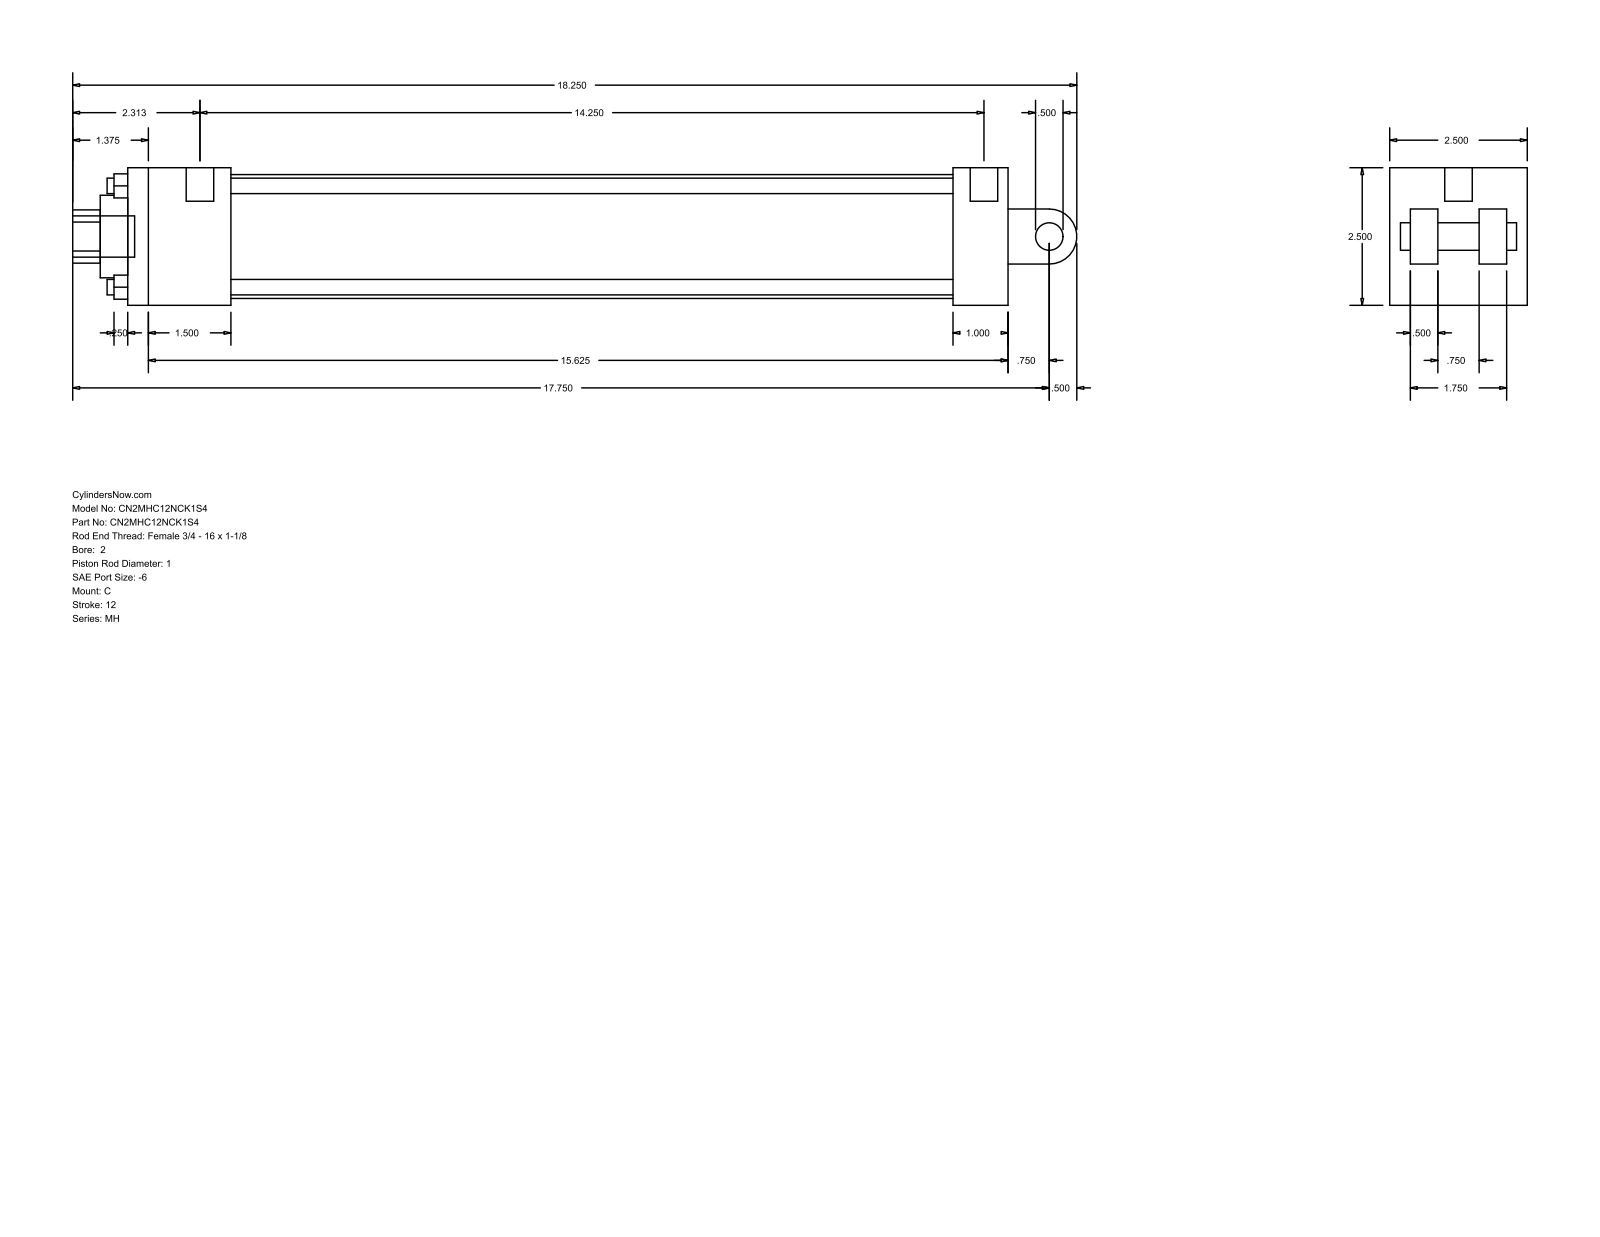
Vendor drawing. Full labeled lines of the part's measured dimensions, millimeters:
Part name (STEP PRODUCT): MH_C__0200_1
STEP written by: GSSL Pune (CONFIG_CONTROL_DESIGN)
Units: millimetres
Bodies: 0 solids, 99 faces (70 planar, 29 cylindrical, 0 other)
Overall size (bounding box): 463.55 × 63.5 × 63.5
Round holes (diameter × count): ⌀7.14 ×4, ⌀5.56 ×2, ⌀12.7 ×1, ⌀25.4 ×1, ⌀38.1 ×1, ⌀57.15 ×1
Round bosses / shafts (diameter × count): ⌀12.7 ×2, ⌀5.56 ×2, ⌀19.05 ×1
Partial cylindrical surfaces — rounded edges, fillets, slot ends (radius × count): R12.29 ×1, R12.7 ×1
Main face-to-face distances: 63.5, 406.4, 12.7, 25.4, 9.52, 47.63, 53.98, 381, 333.37, 358.77
Hole centre spacings: 33.05, 46.74, 66.1, 3.17
